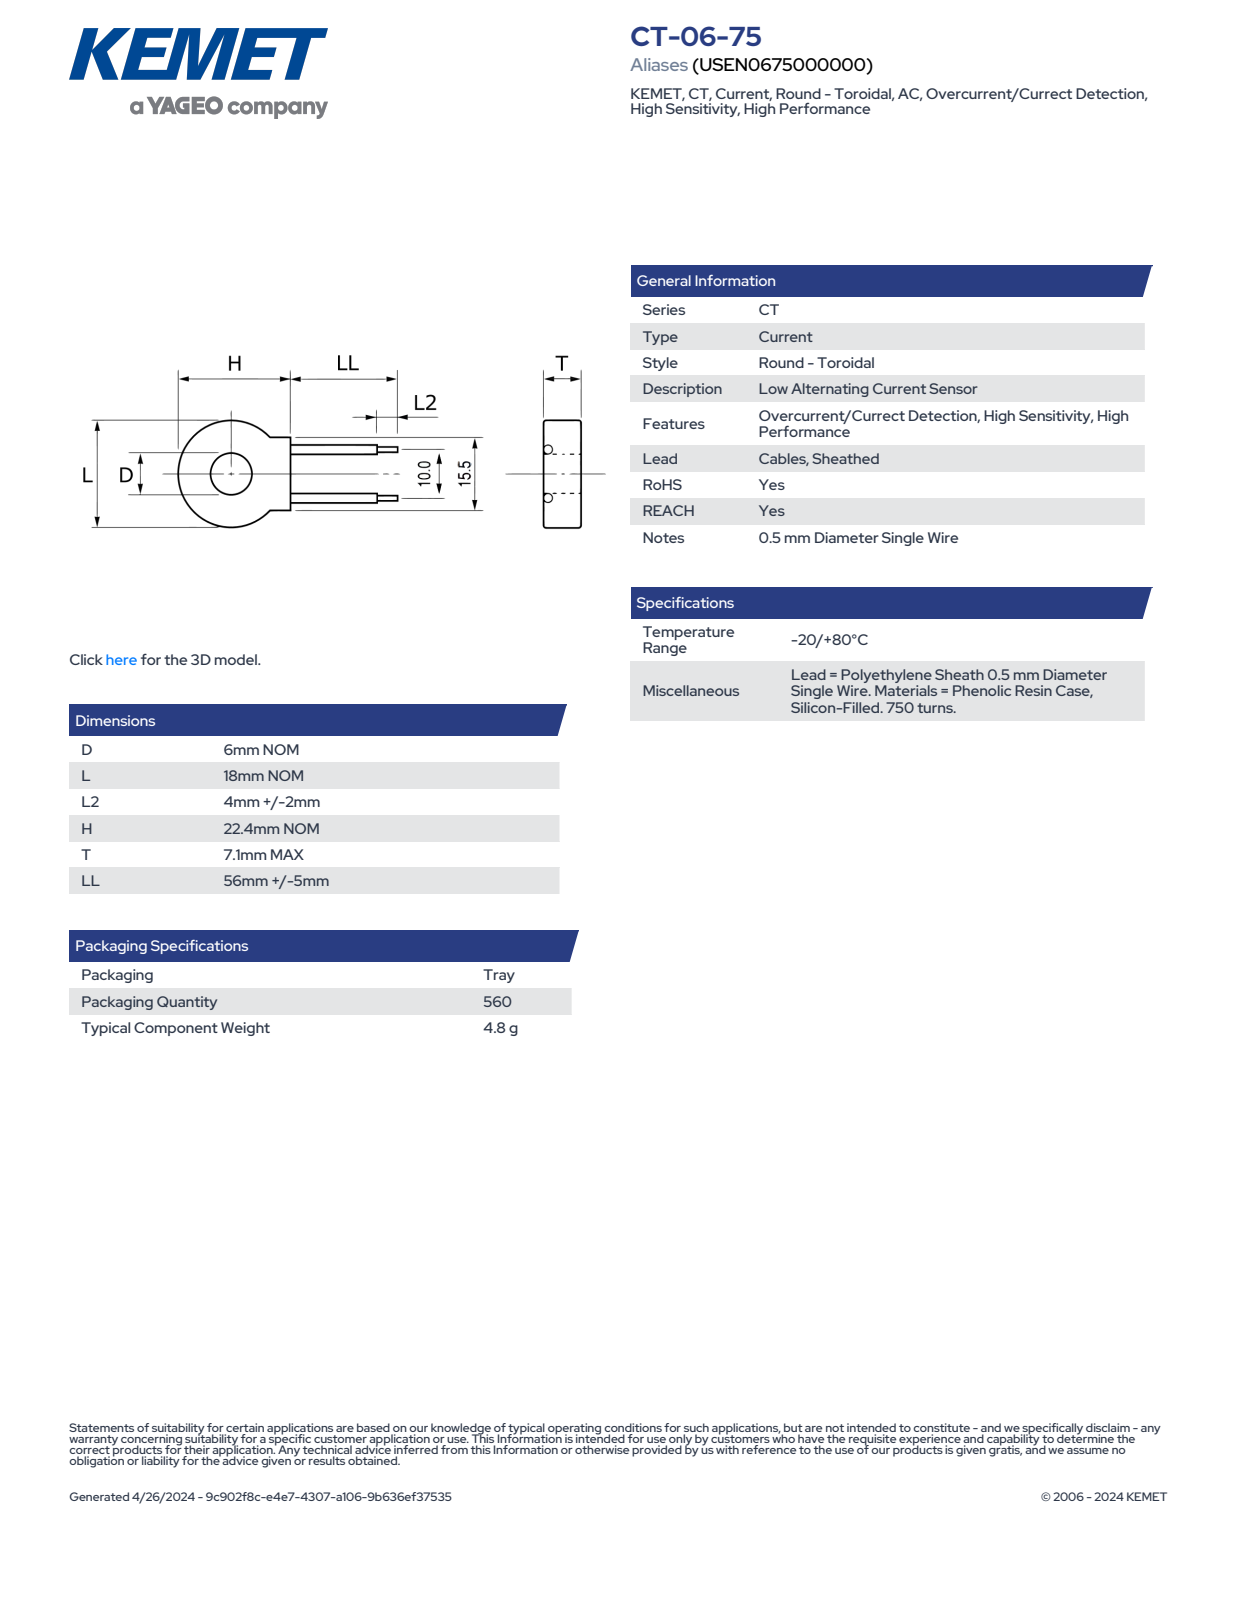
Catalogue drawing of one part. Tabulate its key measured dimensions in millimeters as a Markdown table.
| quantity | value |
| --- | --- |
| part name | SC_CT06_D6L17.8L26H22.4T7.1LL61 |
| STEP written by | SolidWorks 2014 (AUTOMOTIVE_DESIGN) |
| units | millimeters |
| bodies | 1 solid, 78 faces (31 planar, 16 cylindrical, 31 other) |
| overall size | 83.4 × 17.8 × 7.1 |
| volume | 2 420 mm³ |
| surface area | 1 818 mm² |
| round holes (diameter × count) | 6 × 1 |
| round bosses / shafts (diameter × count) | 1.5 × 2, 1 × 2 |
| partial cylindrical surfaces (radius × count) | 8.89 × 1, 8.9 × 1 |
| main face-to-face distances | 7.1, 15.5, 55, 61, 6, 2.54, 4.56, 2.02, 2.93, 4.17 |
